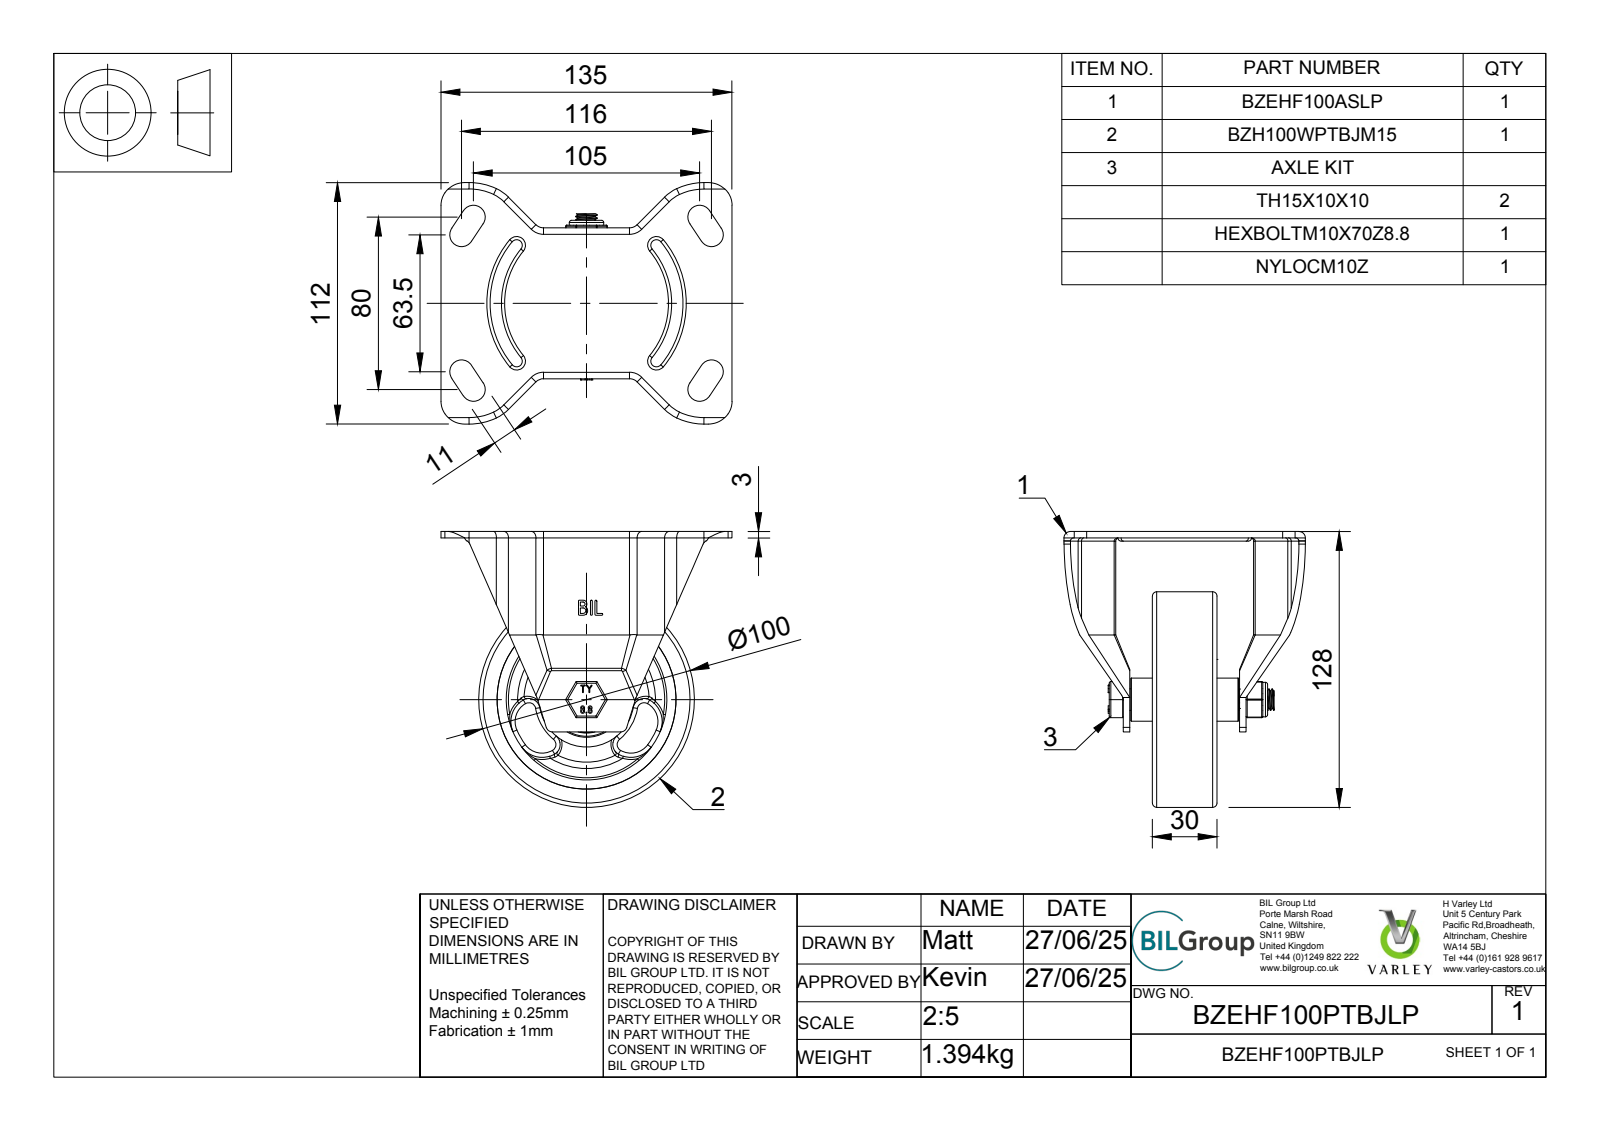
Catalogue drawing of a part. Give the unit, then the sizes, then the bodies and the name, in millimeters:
Units: millimetres
Overall size (bounding box): 135 × 128 × 112
Round holes (diameter × count): ⌀10 ×1, ⌀10.2 ×1, ⌀10.5 ×1, ⌀12 ×1, ⌀15 ×1, ⌀22.5 ×1, ⌀30 ×1, ⌀31 ×1, ⌀32 ×1, ⌀35 ×1, ⌀74.5 ×1, ⌀83 ×1
Round bosses / shafts (diameter × count): ⌀100 ×1, ⌀44 ×1, ⌀30.5 ×1, ⌀23 ×1, ⌀20 ×1, ⌀19 ×1, ⌀18 ×1, ⌀16 ×1
Partial cylindrical surfaces — rounded edges, fillets, slot ends (radius × count): R0.5 ×18, R3 ×13, R5.12 ×12, R11.64 ×12, R1.5 ×8, R5.5 ×8, R10 ×8, R0.75 ×6
Main face-to-face distances: 3, 30, 20, 60.5, 6.5, 17, 47, 67, 50, 9.5
Volume: 253 184 mm³ · Surface area: 134 249 mm²
Bodies: 35 solids, 1288 faces (432 planar, 269 cylindrical, 587 other)
Part name (STEP PRODUCT): BZEHF100PTBJLP v4; BZEHF100ASLP v1; ZINC PLATED, PRESSED STEEL BRACKET; BZH100WPTBJM15 v1 (+7 more)
STEP written by: Autodesk Translation Framework v14.10.0.0 (AUTOMOTIVE_DESIGN)
